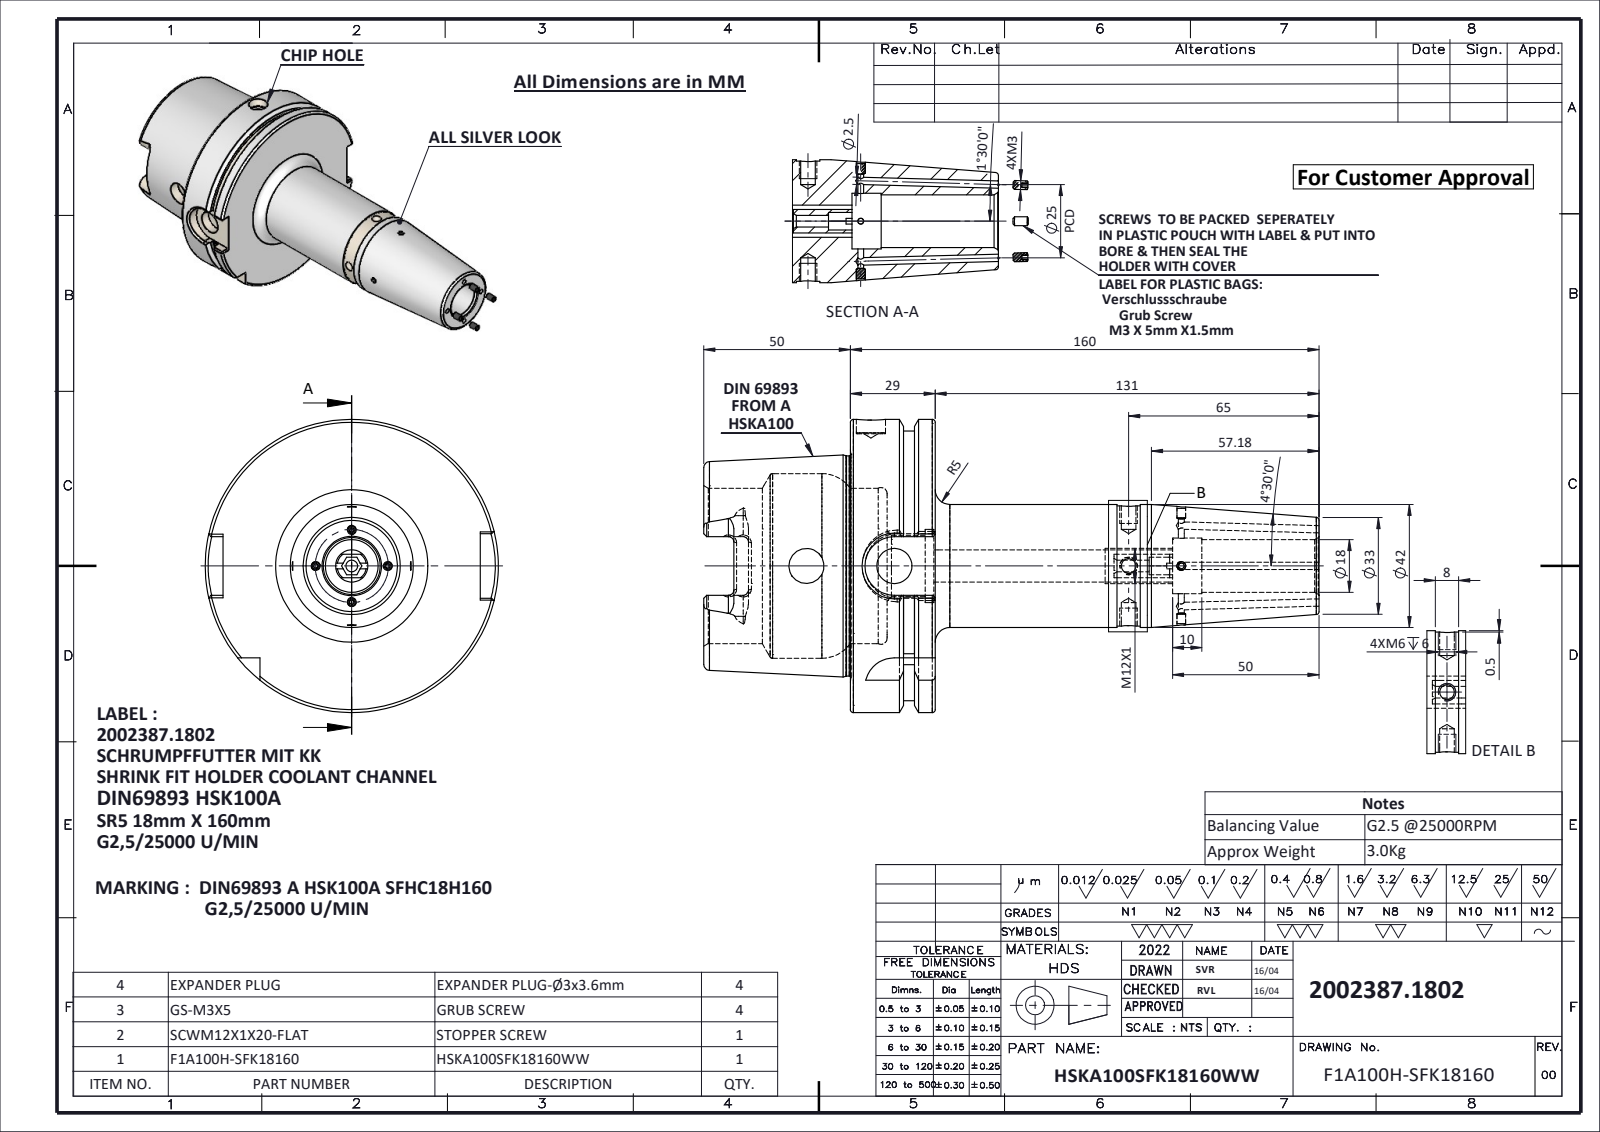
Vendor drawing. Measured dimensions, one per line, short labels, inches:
name: GS-M3X5; HSKA100SFK18160WW; EXPANDER PLUG Ø3x3.6; F1A100H-SFK18160 (+1 more)
written by: SolidWorks 2024 (CONFIG_CONTROL_DESIGN)
unit: in
bodies: 10 solids, 389 faces (137 planar, 116 cylindrical, 136 other)
size: 8.661 × 3.937 × 3.937
volume: 24.32 in³; area: 116.3 in²
holes: 4× ⌀0.098, 2× ⌀0.079, 2× ⌀0.118, 2× ⌀0.197, 2× ⌀0.472, 1× ⌀0.157, 1× ⌀0.394, 1× ⌀0.433, 1× ⌀0.709, 1× ⌀0.748, 1× ⌀0.827, 1× ⌀0.984
bosses: 4× ⌀0.118, 1× ⌀3.937, 1× ⌀3.622, 1× ⌀2.959, 1× ⌀1.654, 1× ⌀1.614
rounds: 6× R0.071, 4× R0.192, 2× R0.394, 1× R0.236, 1× R0.433
face distances: 1.14, 0.492, 0.648, 1.969, 2.461, 3.108, 6.297, 8.266, 5.805, 5.157
hole spacings: 0.709, 1.181, 3.148, 3.463, 3.856, 4.171, 4.329, 5.037
